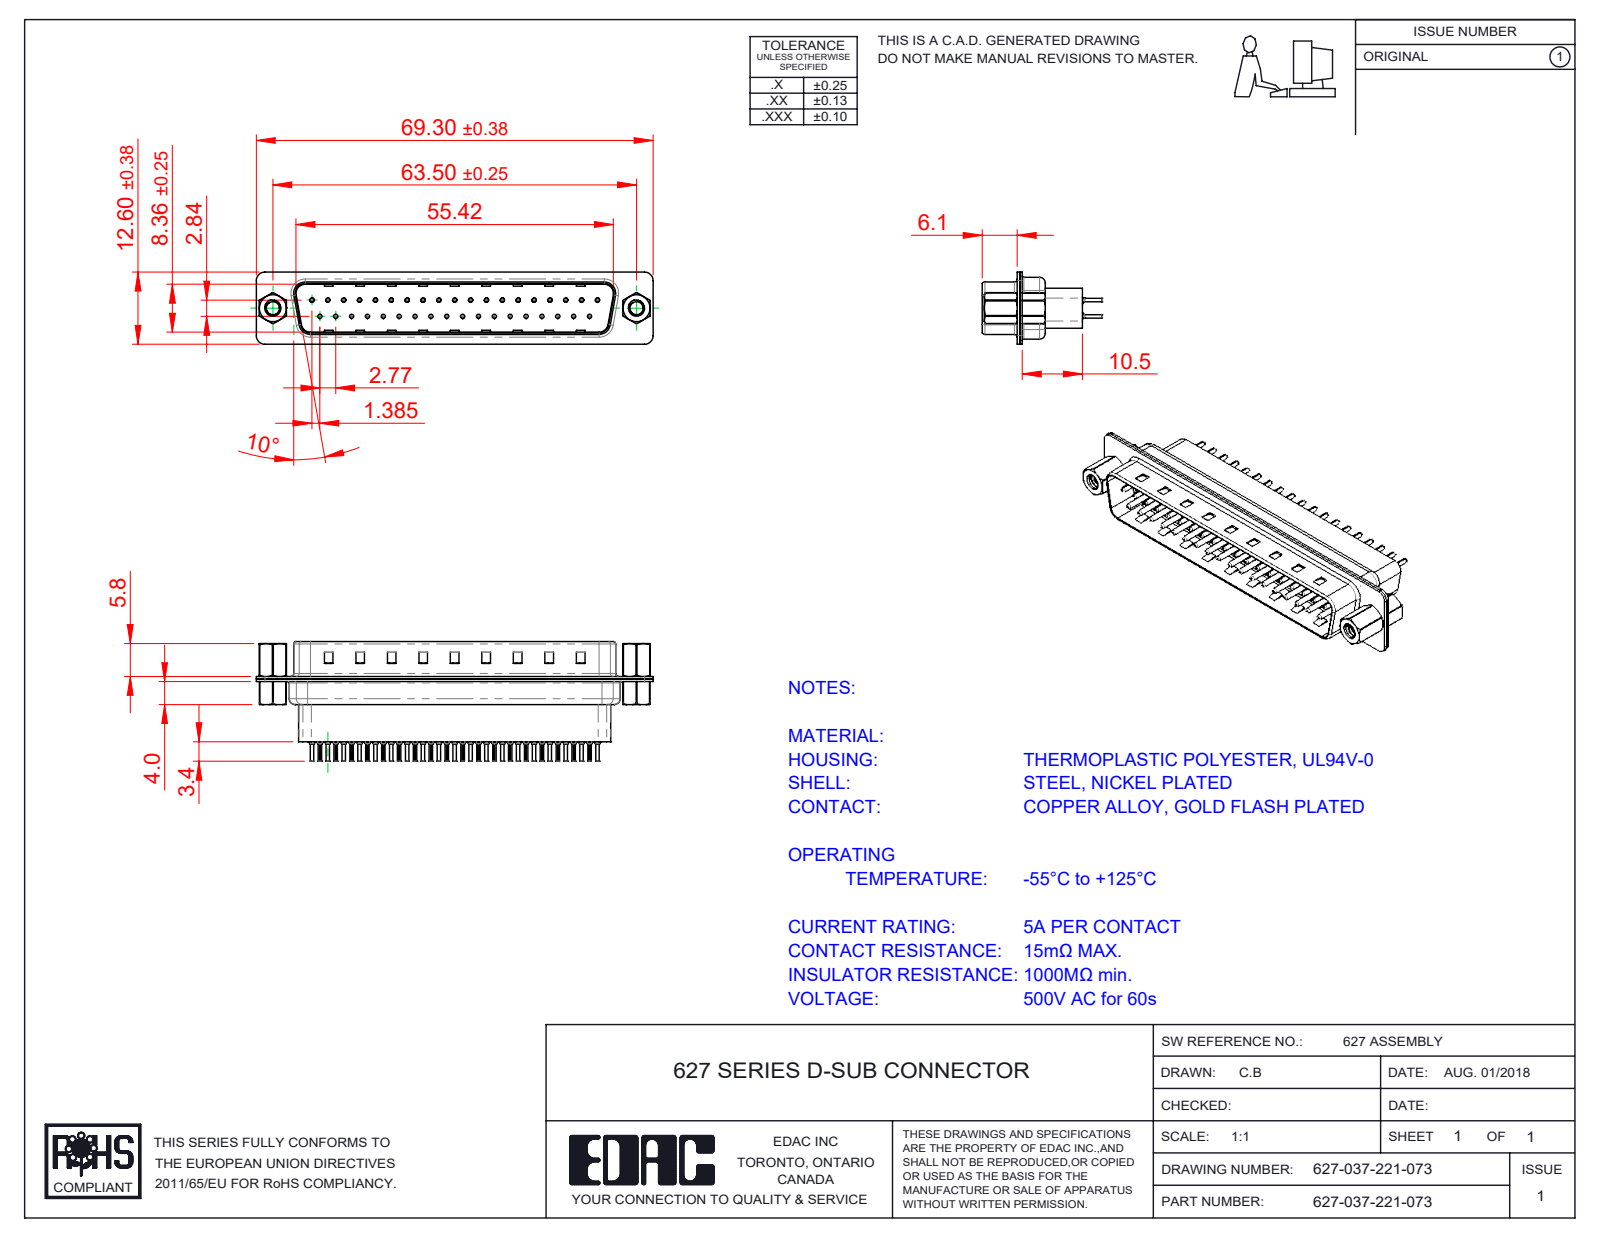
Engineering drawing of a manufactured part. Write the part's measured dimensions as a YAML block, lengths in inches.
part_name: "627-037-221-073; 627 Shell Rear_37 Contacts; 627 Contact Row 1_21H; 627 4-40 Hex Standoff (+4 more)"
step_written_by: "SolidWorks 2020 (CONFIG_CONTROL_DESIGN)"
units: inches
bodies: {solids: 44, faces: 4160, planar: 1113, cylindrical: 1580, other: 1467}
overall_size: [2.728, 0.819, 0.496]
volume: 0.336
surface_area: 21.75
round_holes:
  - {diameter: 0.008, count: 37}
  - {diameter: 0.014, count: 37}
  - {diameter: 0.043, count: 37}
  - {diameter: 0.063, count: 37}
  - {diameter: 0.089, count: 2}
  - {diameter: 0.09, count: 2}
  - {diameter: 0.157, count: 2}
  - {diameter: 0.189, count: 2}
round_bosses_or_shafts:
  - {diameter: 0.079, count: 37}
  - {diameter: 0.059, count: 37}
  - {diameter: 0.03, count: 37}
  - {diameter: 0.024, count: 37}
  - {diameter: 0.197, count: 2}
  - {diameter: 0.193, count: 2}
  - {diameter: 0.11, count: 2}
partial_cylinders:
  - {radius: 0.004, count: 74}
  - {radius: 0.059, count: 16}
  - {radius: 0.079, count: 12}
  - {radius: 0.02, count: 8}
  - {radius: 0.063, count: 8}
  - {radius: 0.01, count: 4}
  - {radius: 0.024, count: 4}
  - {radius: 0.026, count: 4}
face_to_face_distances: [0.016, 0.032, 0.377, 0.018, 0.027, 0.302, 0.059, 0.043, 0.318, 0.345]
hole_center_spacings: [0.124, 0.109, 0.218, 0.327, 0.198, 0.398, 0.436, 0.503]
